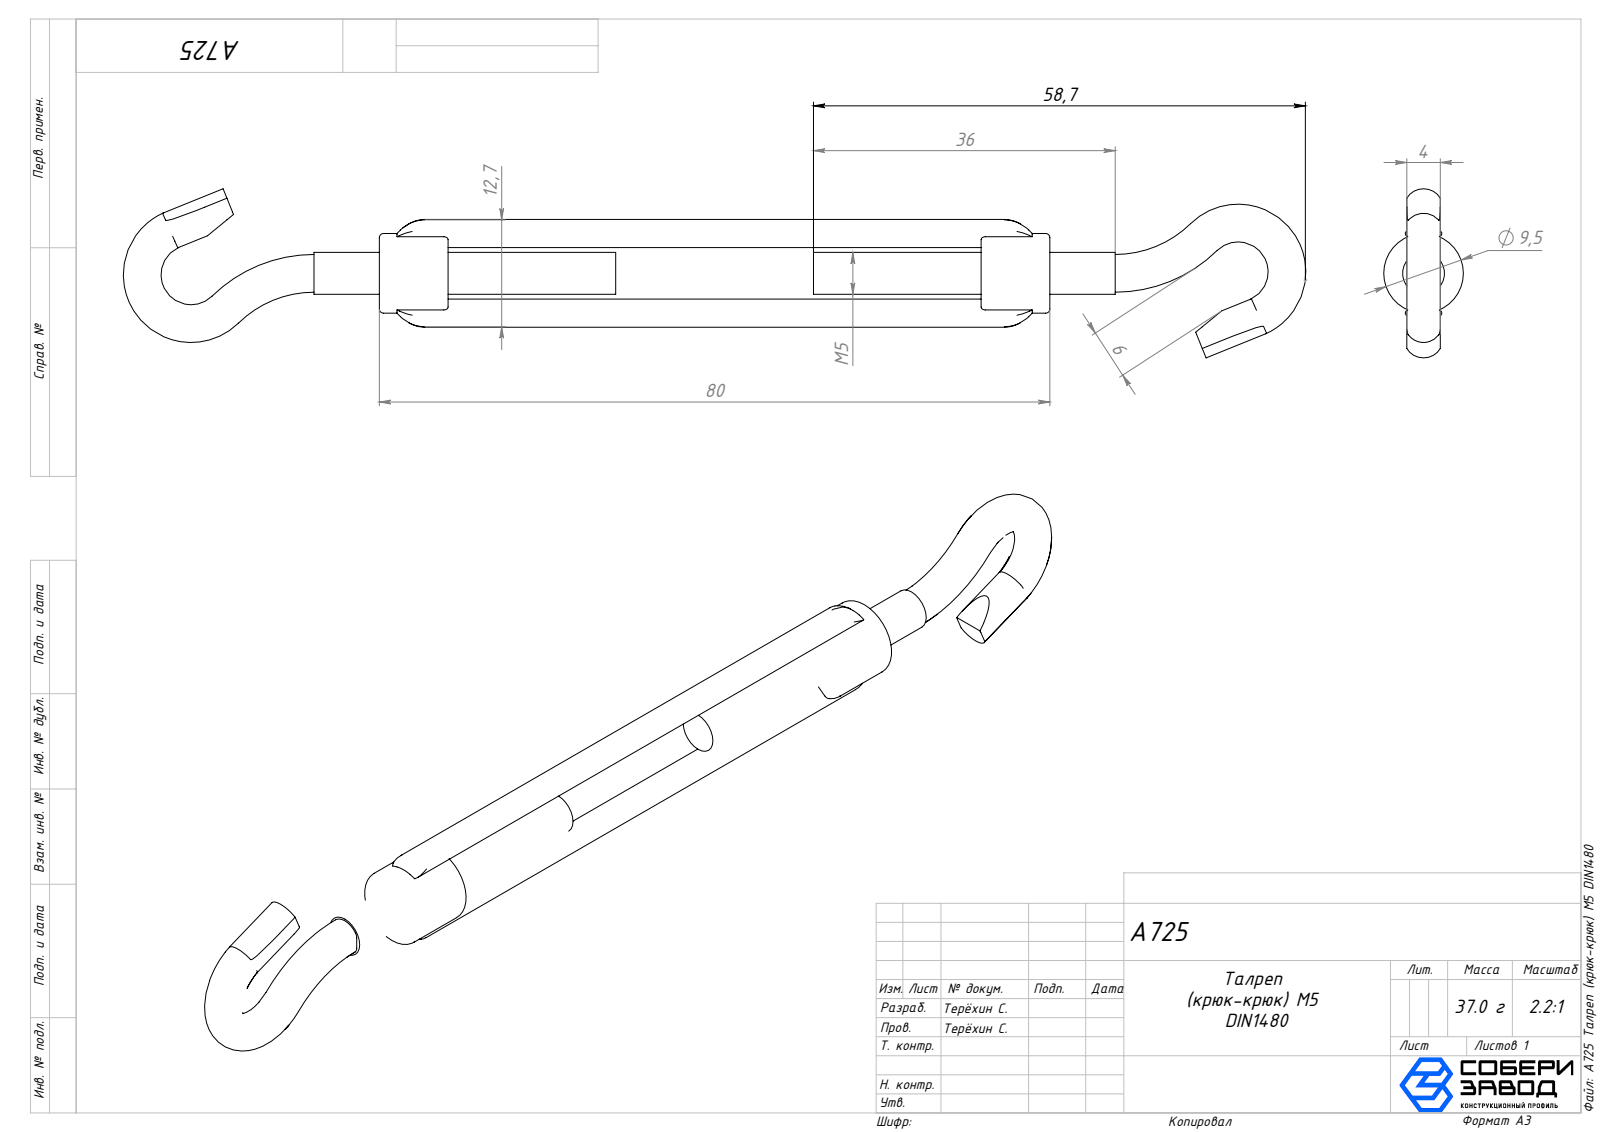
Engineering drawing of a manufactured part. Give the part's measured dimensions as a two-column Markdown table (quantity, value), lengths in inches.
| quantity | value |
| --- | --- |
| part name | Талреп крюк_00; Талреп основание_00; A725 Талреп (крюк-крюк) М5 DIN1480_00; Сборка1 |
| STEP written by | SolidWorks 2025 (AUTOMOTIVE_DESIGN) |
| units | inches |
| bodies | 3 solids, 110 faces (24 planar, 32 cylindrical, 54 other) |
| overall size | 5.555 × 0.794 × 0.374 |
| volume | 0.288 in³ |
| surface area | 7.277 in² |
| round holes (diameter × count) | 0.157 × 1 |
| round bosses / shafts (diameter × count) | 0.374 × 1, 0.197 × 1 |
| partial cylindrical surfaces (radius × count) | 0.012 × 8, 0.039 × 4, 0.089 × 2 |
| main face-to-face distances | 0.111, 0.302, 0.413, 0.111, 0.191, 0.302, 0.191, 0.157, 0.323, 2.827 |
